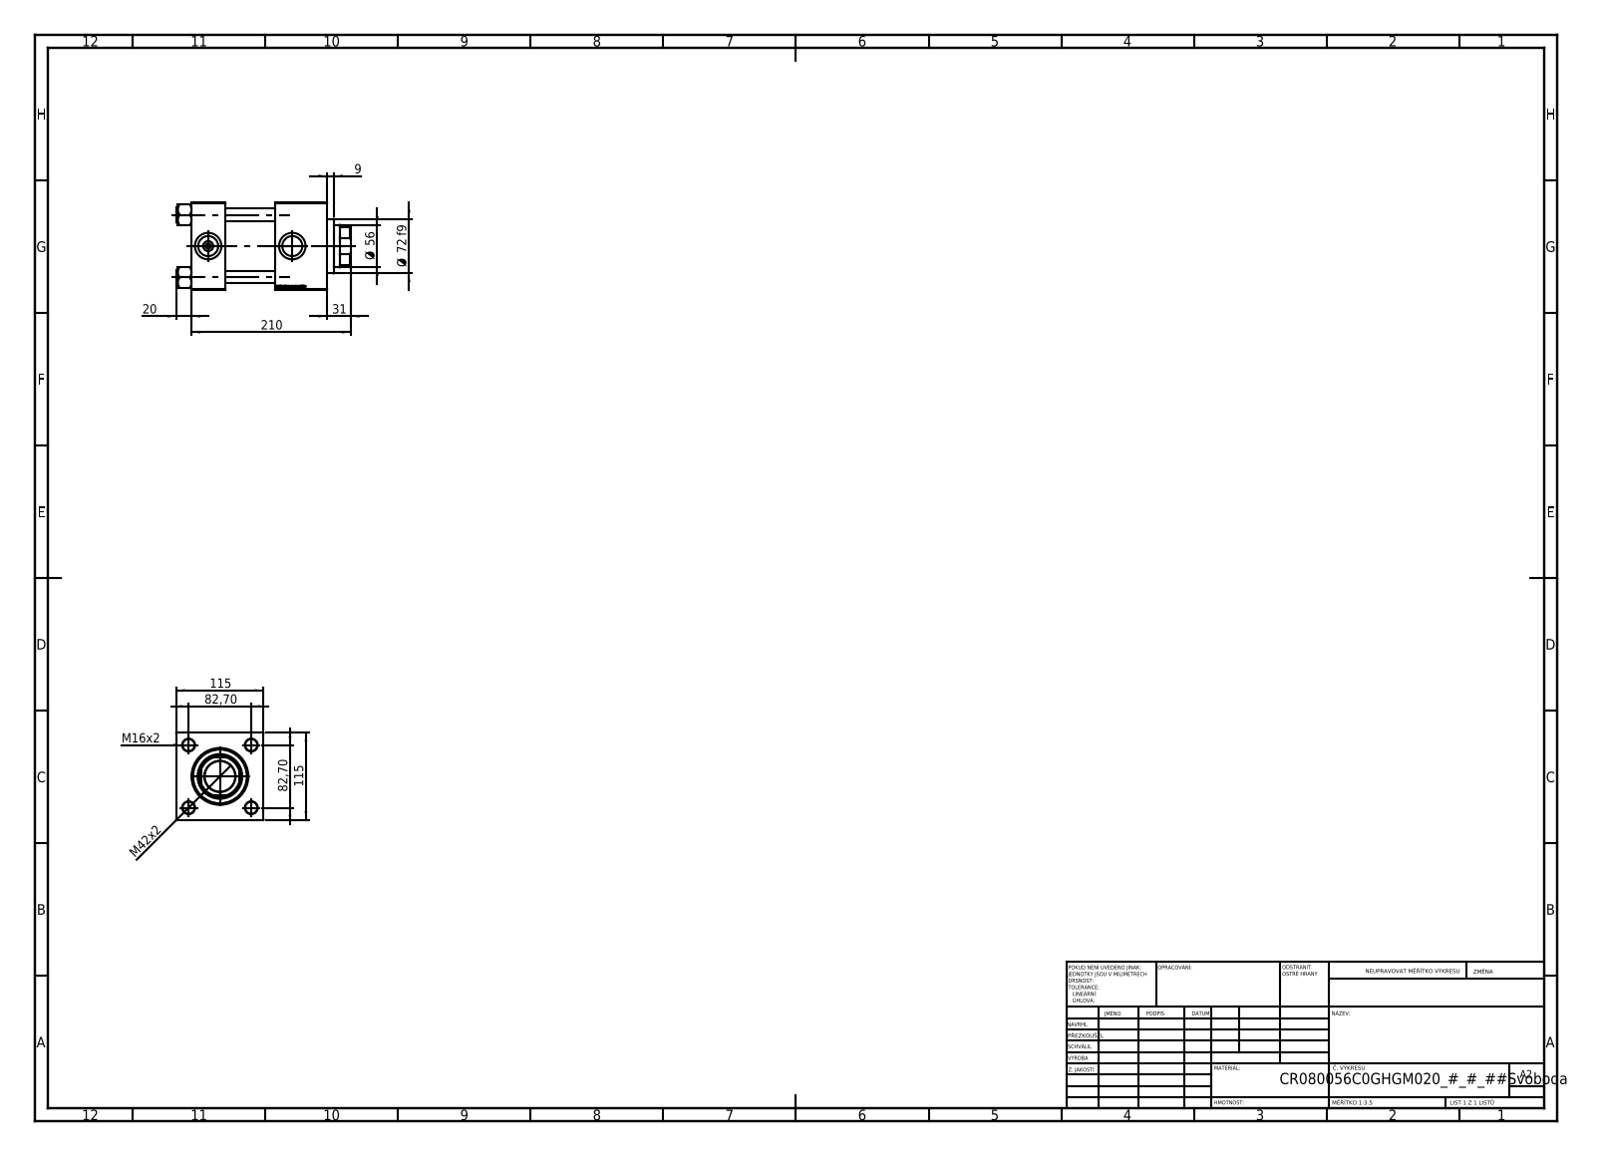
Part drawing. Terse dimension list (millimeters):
name: V215CR_C_TYCINKA; V215CR_VCP_C; V215_VC_A; V215CR_C_Body (+1 more)
written by: SolidWorks 2019 (CONFIG_CONTROL_DESIGN)
unit: mm
bodies: 11 solids, 1193 faces (573 planar, 84 cylindrical, 536 other)
size: 230 × 115 × 115
volume: 1 862 000 mm³; area: 280 215 mm²
holes: 4× ⌀16, 2× ⌀7, 2× ⌀26.44, 2× ⌀35, 1× ⌀40.5, 1× ⌀56, 1× ⌀59, 1× ⌀61, 1× ⌀72, 1× ⌀80
bosses: 4× ⌀19, 1× ⌀86
rounds: 1× R27
face distances: 115, 44, 110, 66, 179, 135, 69, 20, 150.3, 106.3
hole spacings: 58.48, 82.7, 116.96, 111
